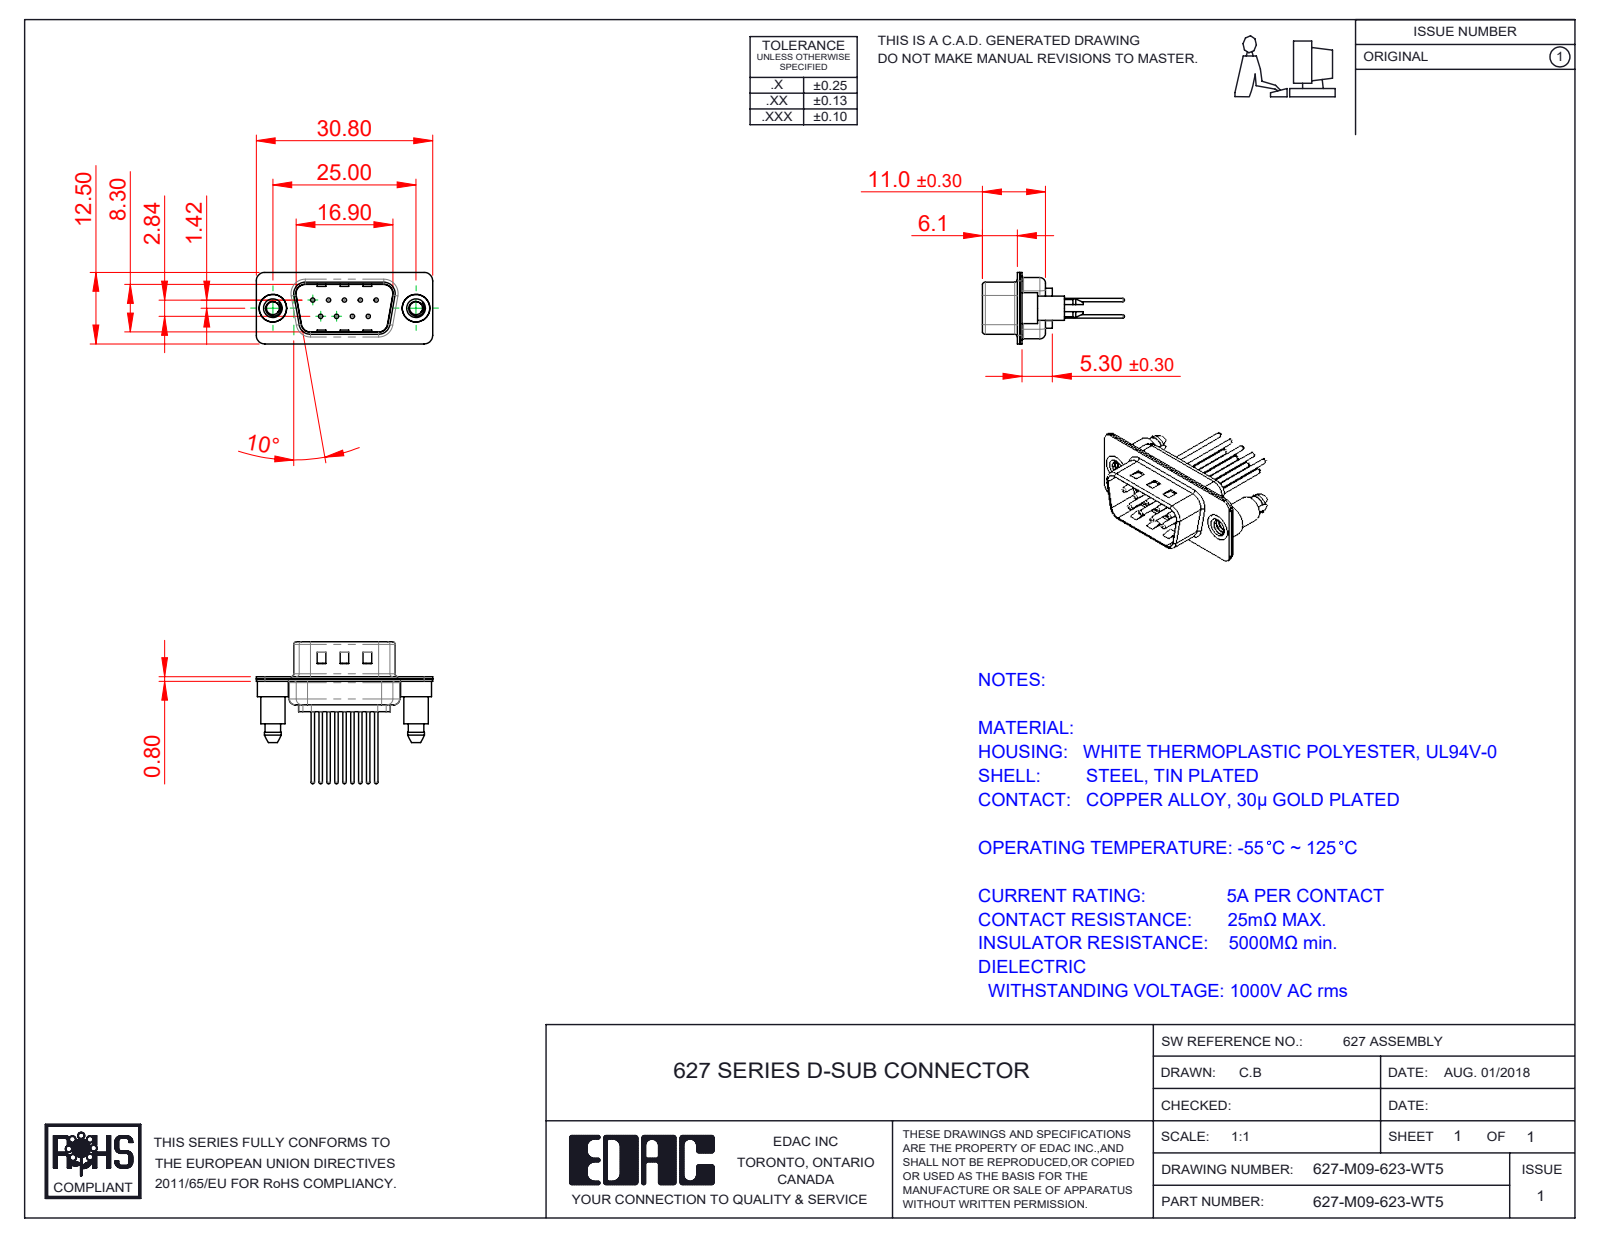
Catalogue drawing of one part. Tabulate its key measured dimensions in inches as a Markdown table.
| quantity | value |
| --- | --- |
| part name | 627M Contact Row 1_23; 627M Contact Row 2_23; 627M Shell Front_09 Contacts; 627M Housing_09 Contacts (+3 more) |
| STEP written by | SolidWorks 2020 (CONFIG_CONTROL_DESIGN) |
| units | inches |
| bodies | 14 solids, 687 faces (186 planar, 287 cylindrical, 214 other) |
| overall size | 1.213 × 0.975 × 0.492 |
| volume | 0.089 in³ |
| surface area | 6.237 in² |
| round holes (diameter × count) | 0.03 × 9, 0.063 × 9, 0.079 × 9, 0.089 × 2, 0.157 × 2, 0.189 × 2 |
| round bosses / shafts (diameter × count) | 0.059 × 9, 0.024 × 9, 0.213 × 2, 0.193 × 2, 0.167 × 2 |
| partial cylindrical surfaces (radius × count) | 0.059 × 18, 0.079 × 12, 0.063 × 10, 0.02 × 8, 0.01 × 4, 0.024 × 4, 0.026 × 4, 0.035 × 4 |
| main face-to-face distances | 0.016, 0.031, 0.374, 0.358, 0.343, 0.026, 0.39, 0.047, 0.209, 0.24 |
| hole center spacings | 0.124, 0.109, 0.218, 0.198, 0.198, 0.327, 0.28, 0.294 |
